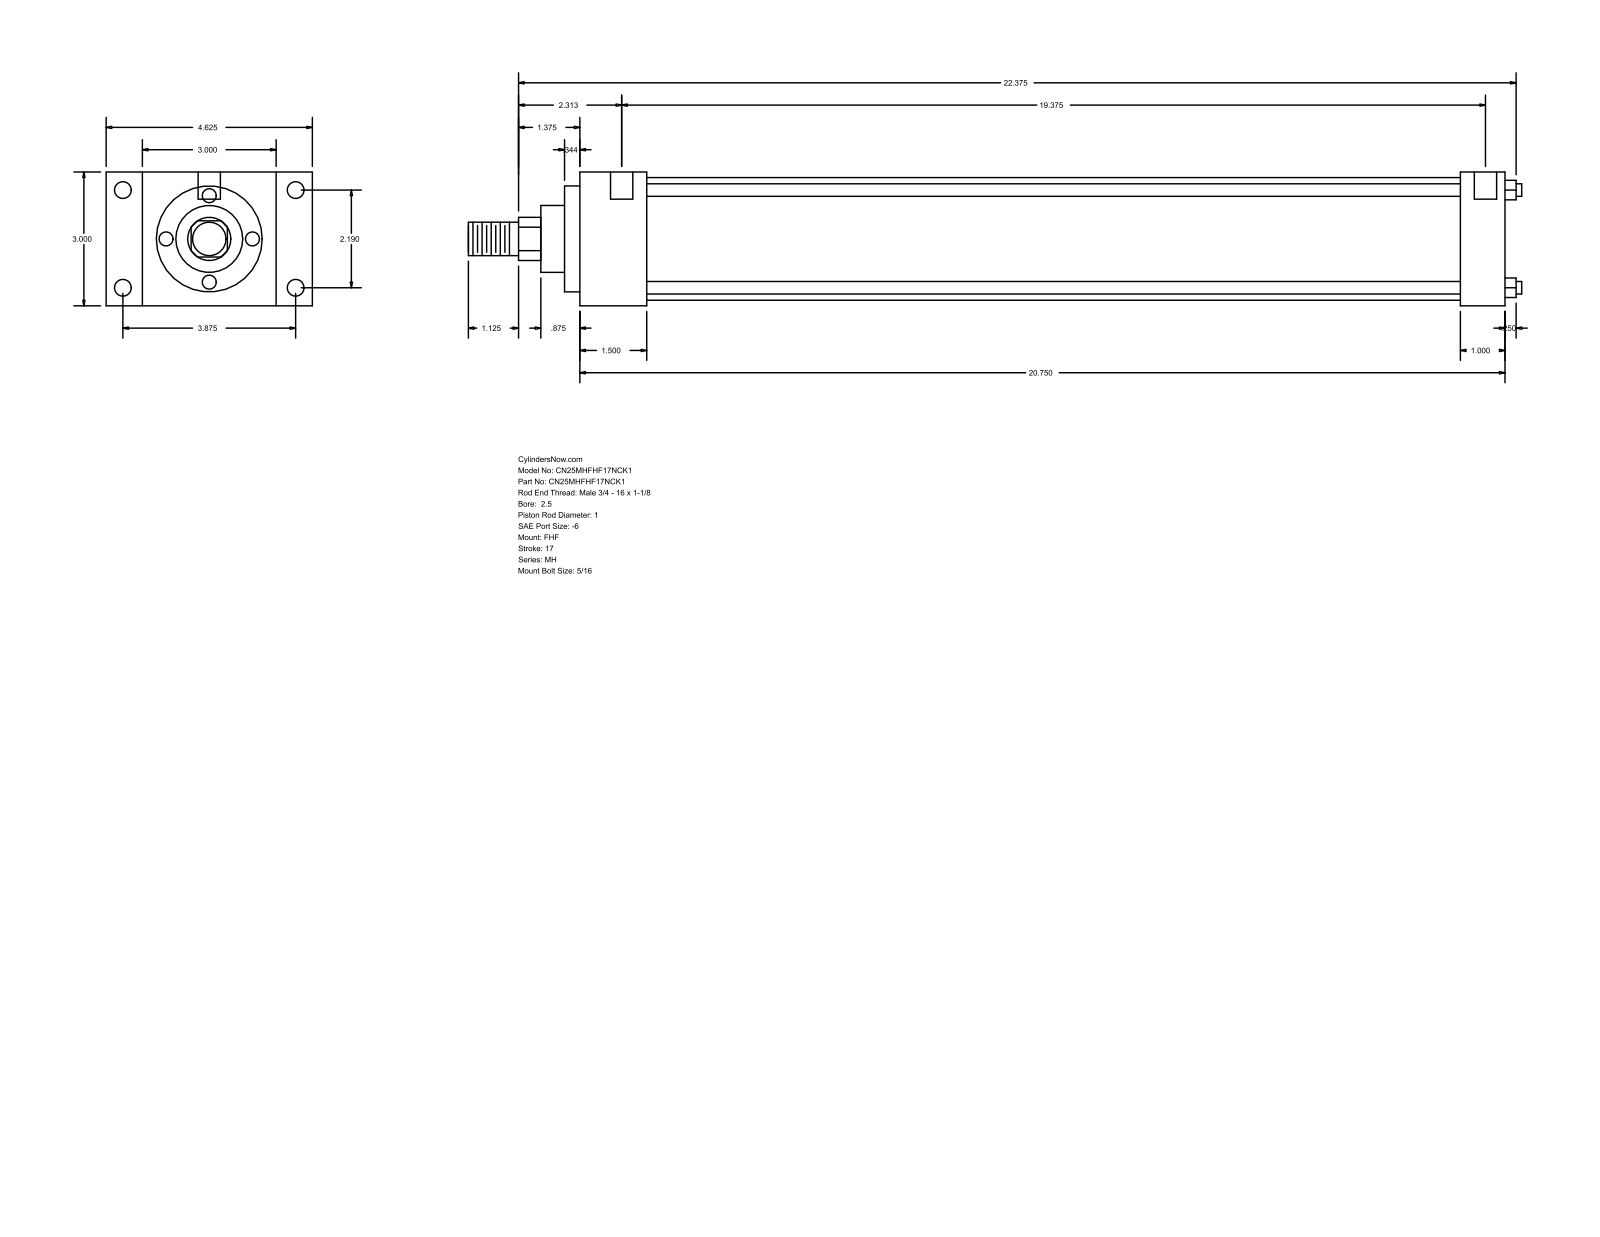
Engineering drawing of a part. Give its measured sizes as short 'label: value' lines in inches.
name: MH_FHF__0250_1
written by: GSSL Pune (CONFIG_CONTROL_DESIGN)
unit: in
bodies: 0 solids, 90 faces (61 planar, 29 cylindrical, 0 other)
size: 23.625 × 4.625 × 3
holes: 4× ⌀0.219, 4× ⌀0.375, 2× ⌀0.5
bosses: 4× ⌀0.281, 1× ⌀2.75, 1× ⌀2.375, 1× ⌀1.5, 1× ⌀1, 1× ⌀0.75
rounds: 1× R0.484
face distances: 3, 20.75, 1.5, 19.25, 0.813, 3.813, 4.625, 19.75, 18.25, 1
hole spacings: 2.19, 3.875, 4.451, 19.687, 0.125, 0.187, 19.375, 19.5
